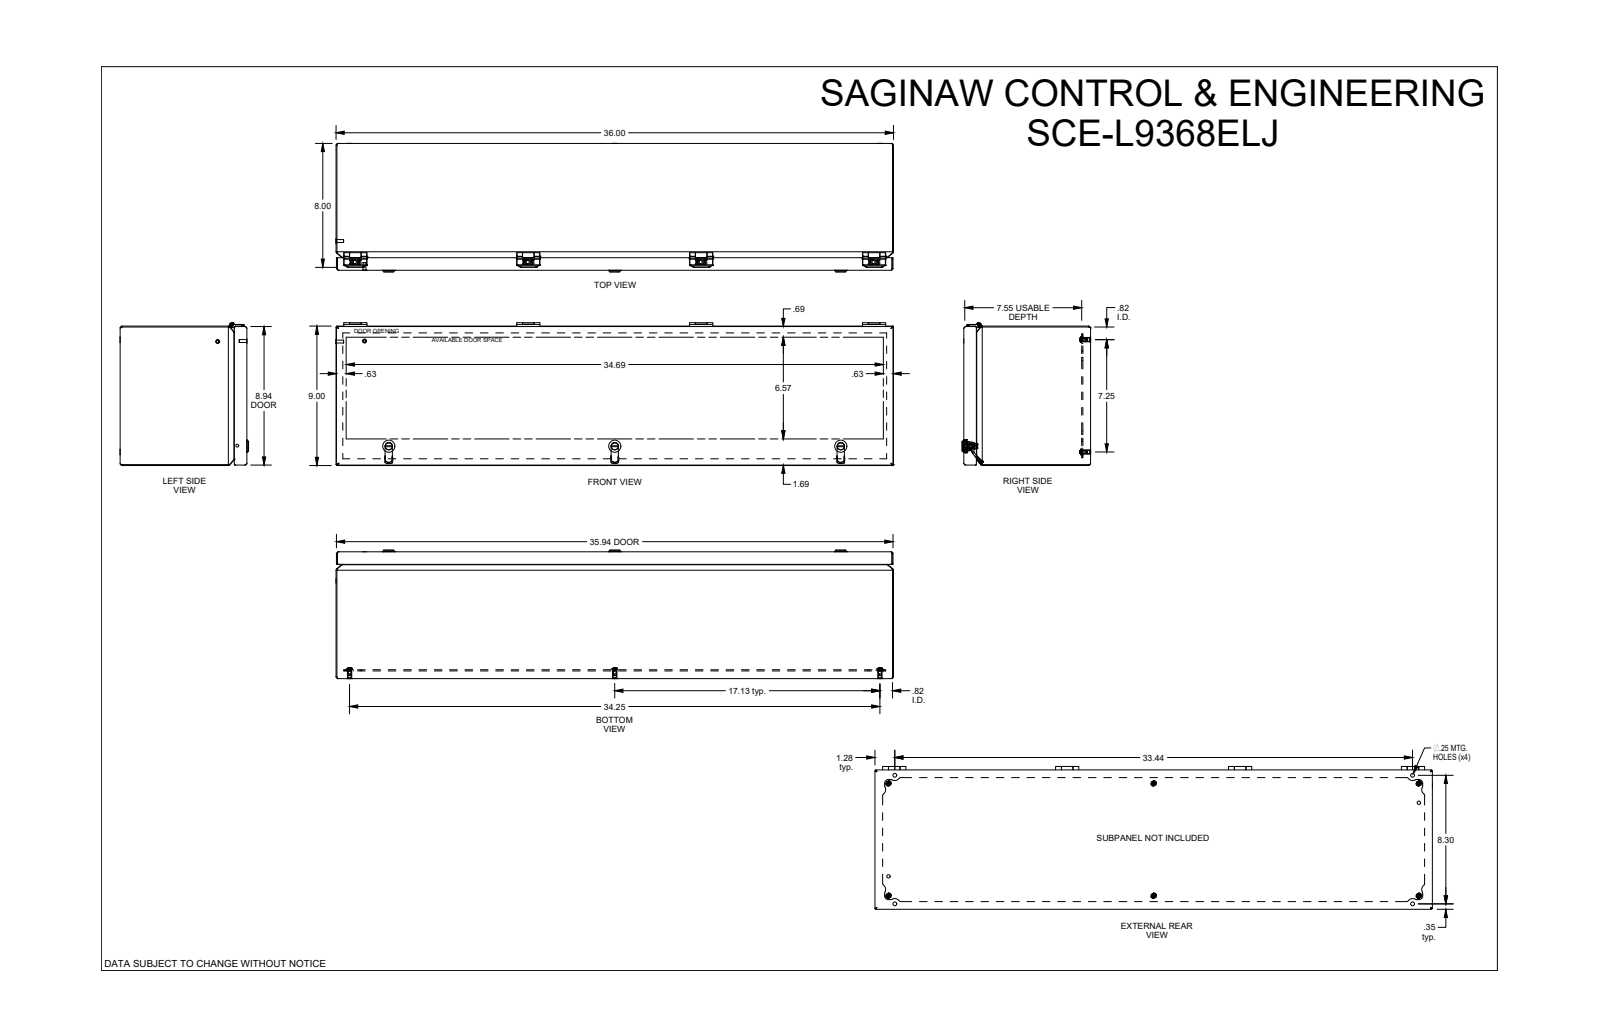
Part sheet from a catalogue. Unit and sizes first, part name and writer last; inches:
Units: inches
Overall size (bounding box): 36.004 × 9.22 × 8.296
Round holes (diameter × count): ⌀0.19 ×6, ⌀0.25 ×6, ⌀0.284 ×6, ⌀0.164 ×4, ⌀0.174 ×4, ⌀0.338 ×4, ⌀0.2 ×3, ⌀0.239 ×3, ⌀0.254 ×3, ⌀0.269 ×3, ⌀0.282 ×3, ⌀0.326 ×3
Round bosses / shafts (diameter × count): ⌀0.188 ×7, ⌀0.373 ×6, ⌀0.28 ×6, ⌀0.26 ×4, ⌀0.15 ×4, ⌀0.788 ×3, ⌀0.548 ×3, ⌀0.46 ×3
Partial cylindrical surfaces — rounded edges, fillets, slot ends (radius × count): R0.008 ×64, R0.02 ×42, R0.01 ×18, R0.05 ×16, R0.25 ×13, R0.125 ×11, R0.031 ×9, R0.062 ×9
Main face-to-face distances: 0.059, 8.941, 0.062, 8.185, 8.126, 8.123, 8.064, 7.614, 0.075, 0.571
Hole centre spacings: 11.167, 17.125, 22.333, 18.596, 7.25, 7.251, 11.167, 14.6
Volume: 114.6 in³ · Surface area: 3 595 in²
Bodies: 55 solids, 2427 faces (1236 planar, 602 cylindrical, 589 other)
Part name (STEP PRODUCT): SCE-L9368ELJ
STEP written by: SolidWorks 2021 (AUTOMOTIVE_DESIGN)
